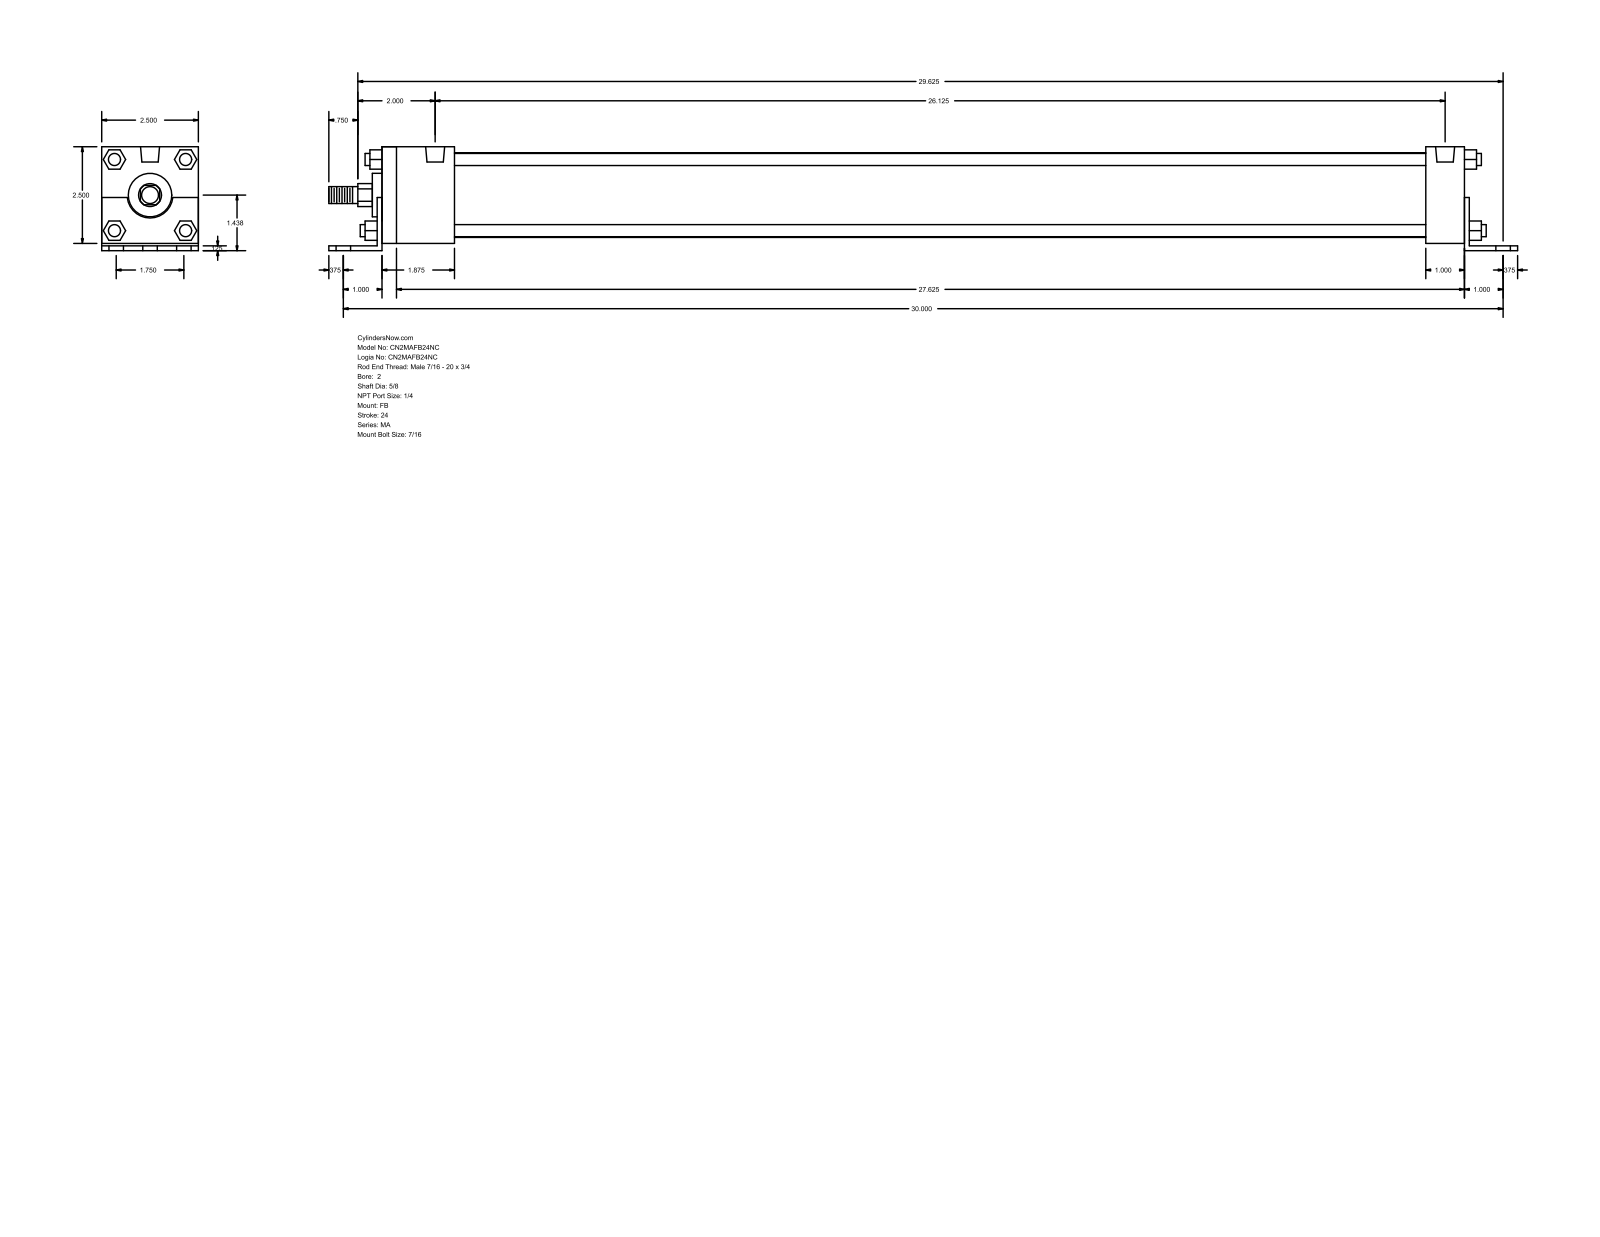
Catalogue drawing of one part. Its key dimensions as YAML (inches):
part_name: "MA_FB__0200_0.625"
step_written_by: "GSSL Pune (CONFIG_CONTROL_DESIGN)"
units: inches
bodies: {solids: 0, faces: 140, planar: 105, cylindrical: 35, other: 0}
overall_size: [30.75, 2.687, 2.5]
round_holes:
  - {diameter: 0.437, count: 6}
  - {diameter: 0.313, count: 4}
  - {diameter: 0.492, count: 2}
round_bosses_or_shafts:
  - {diameter: 0.313, count: 4}
  - {diameter: 2.19, count: 1}
  - {diameter: 1.125, count: 1}
  - {diameter: 0.625, count: 1}
  - {diameter: 0.437, count: 1}
partial_cylinders:
  - {radius: 0.297, count: 1}
  - {radius: 0.593, count: 1}
face_to_face_distances: [2.5, 0.125, 0.187, 2.687, 0.063, 2.563, 28.25, 0.125, 28, 28.125]
hole_center_spacings: [0.875, 30.013, 30, 1.737, 1.75, 2.531, 26.125, 27.639]
